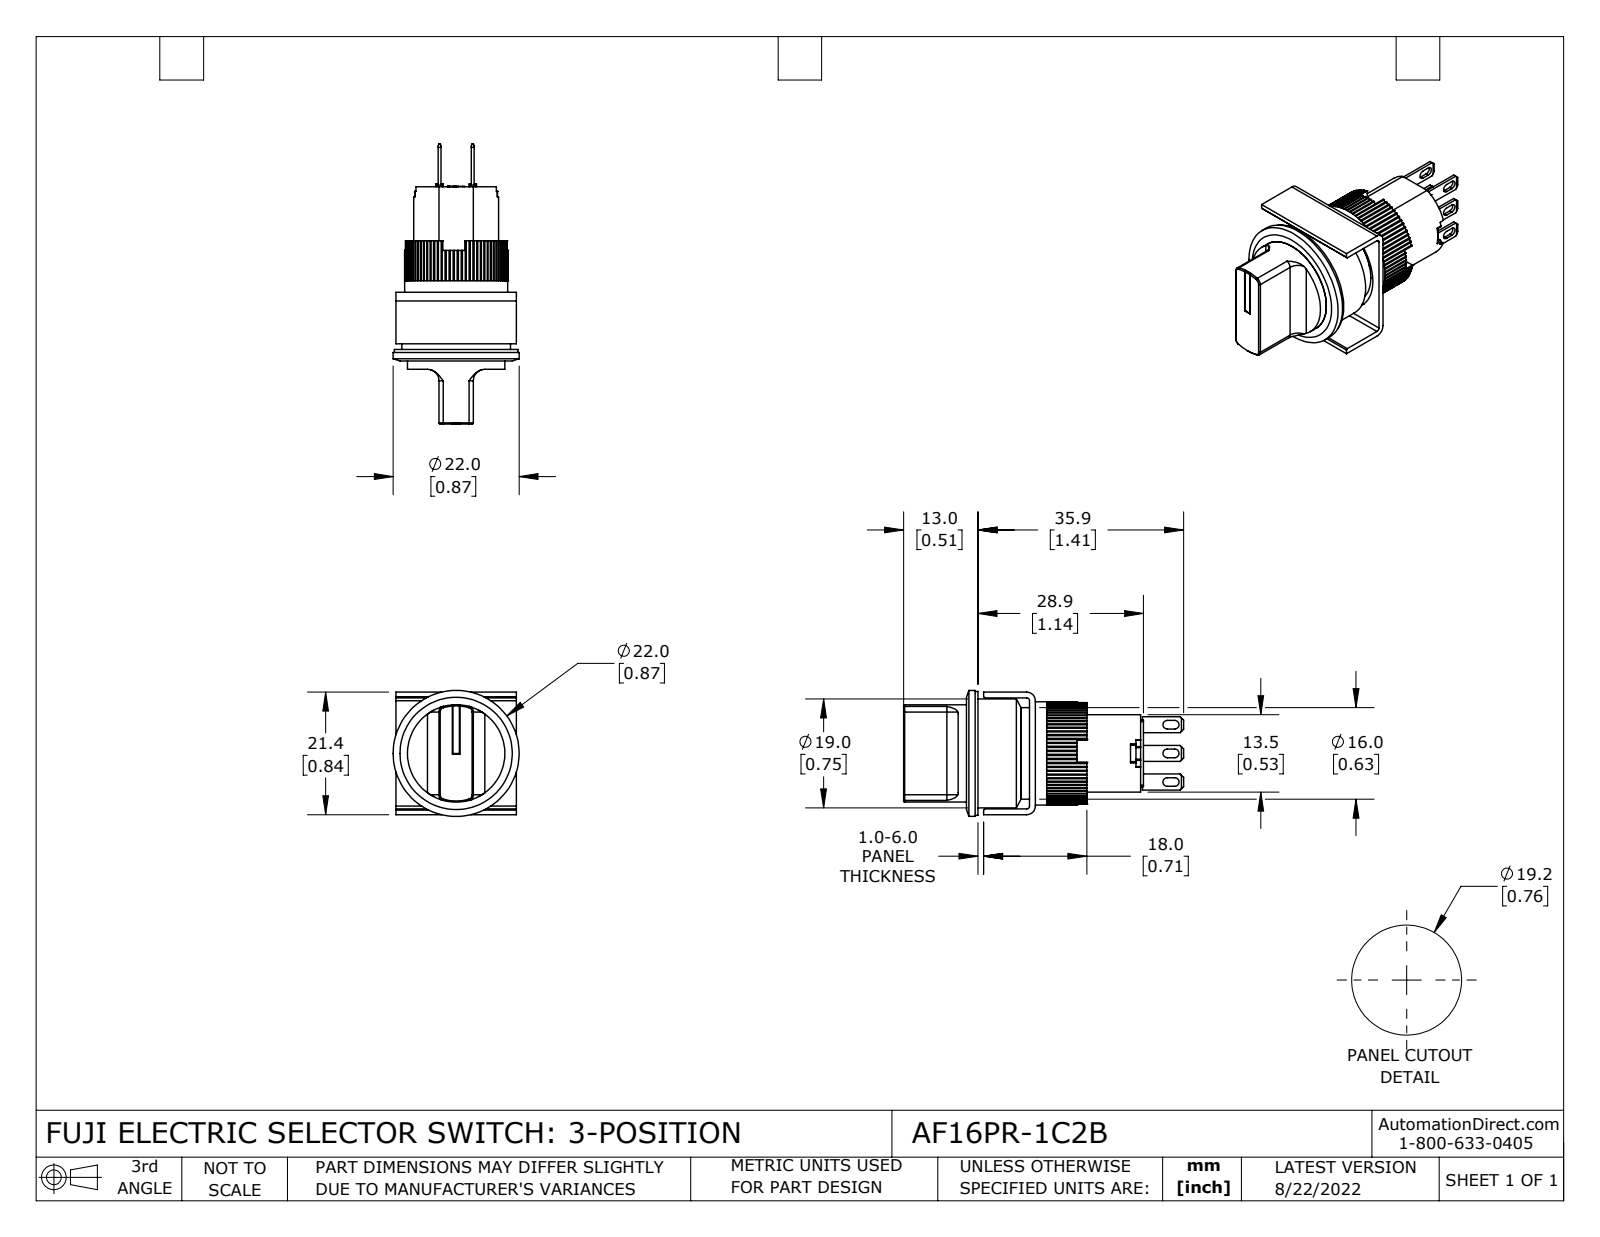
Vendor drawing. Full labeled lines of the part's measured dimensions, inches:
Part name (STEP PRODUCT): AF16PR-1C2B
STEP written by: SolidWorks 2021 (CONFIG_CONTROL_DESIGN)
Units: inches
Bodies: 12 solids, 709 faces (505 planar, 189 cylindrical, 15 other)
Overall size (bounding box): 1.925 × 0.866 × 0.866
Volume: 0.493 in³ · Surface area: 10.41 in²
Round holes (diameter × count): ⌀0.039 ×1, ⌀0.669 ×1, ⌀0.709 ×1, ⌀0.748 ×1
Round bosses / shafts (diameter × count): ⌀0.866 ×1, ⌀0.85 ×1, ⌀0.63 ×1, ⌀0.583 ×1
Partial cylindrical surfaces — rounded edges, fillets, slot ends (radius × count): R0.01 ×80, R0.008 ×14, R0.03 ×6, R0.039 ×4, R0.02 ×2, R0.059 ×2, R0.079 ×2, R0.331 ×1
Main face-to-face distances: 0.374, 0.039, 0.059, 0.803, 0.764, 0.02, 0.433, 0.155, 0.648, 0.232
